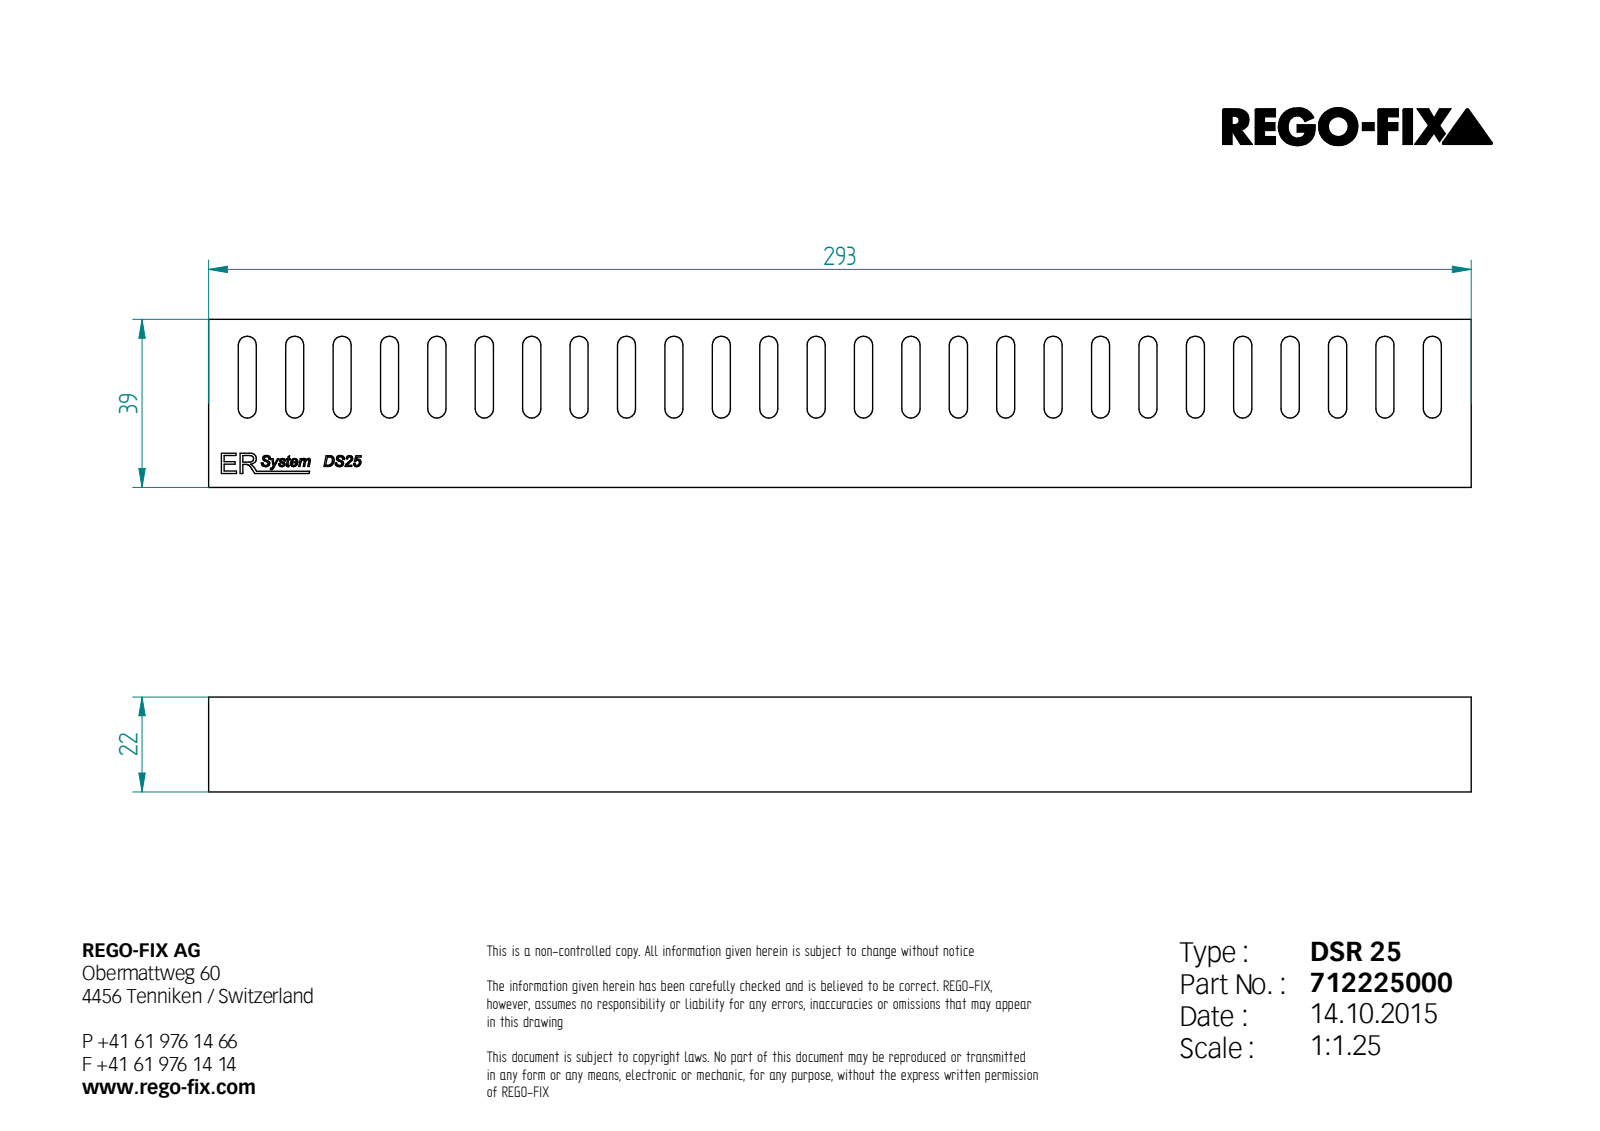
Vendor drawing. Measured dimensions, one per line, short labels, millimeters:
written by: Unknown (AUTOMOTIVE_DESIGN)
unit: mm
bodies: 1 solid, 241 faces (161 planar, 52 cylindrical, 28 other)
size: 293 × 39 × 22
volume: 236 567 mm³; area: 45 846 mm²
rounds: 52× R2.1
face distances: 22, 39, 14.5, 7.5, 11, 33, 4.2, 44, 293, 15.2
